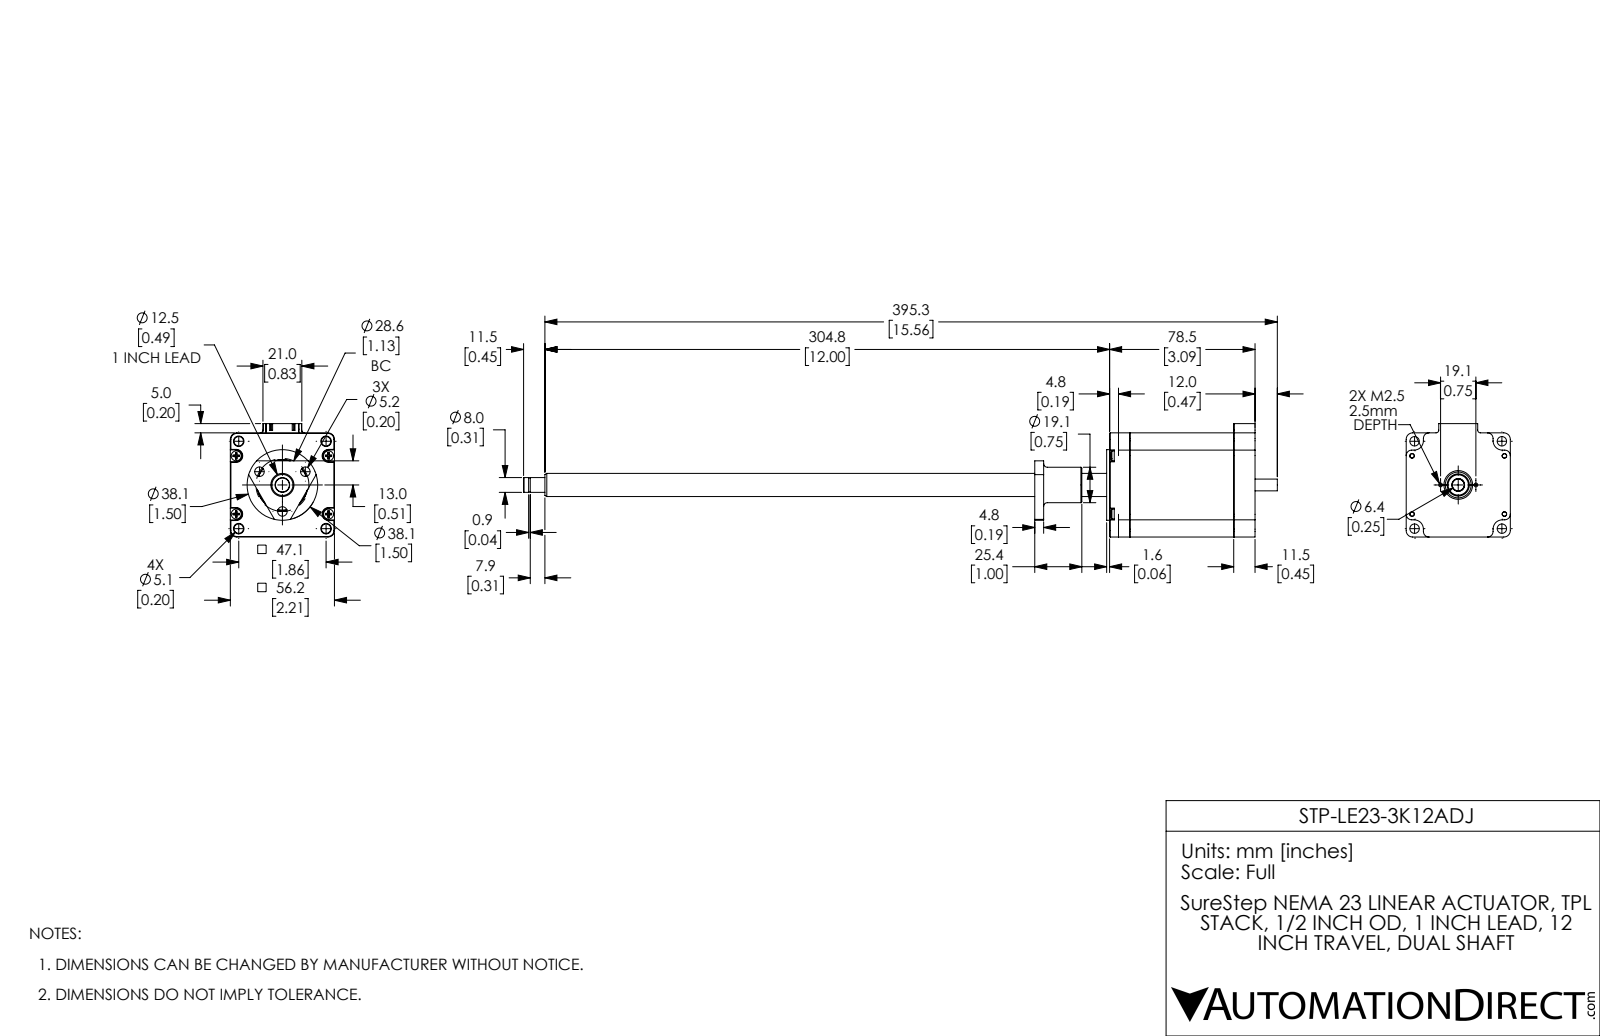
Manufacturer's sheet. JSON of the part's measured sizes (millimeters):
{"part_name": "STP-LE23-3K12ADJ_1; STP-LE23-3K12ADJ; STP-LE23-3K12ADJ_2", "step_written_by": "SolidWorks 2017 (AUTOMOTIVE_DESIGN)", "units": "millimeters", "bodies": {"solids": 7, "faces": 1001, "planar": 380, "cylindrical": 460, "other": 161}, "overall_size": [406.8, 61.2, 56.2], "volume_mm3": 246029, "surface_area_mm2": 69326, "round_holes": [[4.5, 8], [2.5, 4], [3.3, 4], [5.1, 4], [5.16, 3], [2, 2], [2.05, 2], [6.9, 1], [10.5, 1], [14.8, 1], [15.5, 1], [16, 1]], "round_bosses_or_shafts": [[5.4, 4], [2.91, 4], [38.1, 1], [36, 1], [35.6, 1], [34.85, 1], [28, 1], [19.1, 1]], "partial_cylinders_radius": [[1.5, 10], [0.2, 8], [3, 8], [1.8, 4], [3.2, 4], [3.5, 4], [5, 4], [0.6, 1]], "face_to_face_distances": [56.2, 56, 11.5, 67.5, 78.5, 11, 51.4, 67, 1.6, 1.1], "hole_center_spacings": [24.75, 14.12, 33.05, 35.01, 45.74, 48.53, 56.99, 6.55]}
